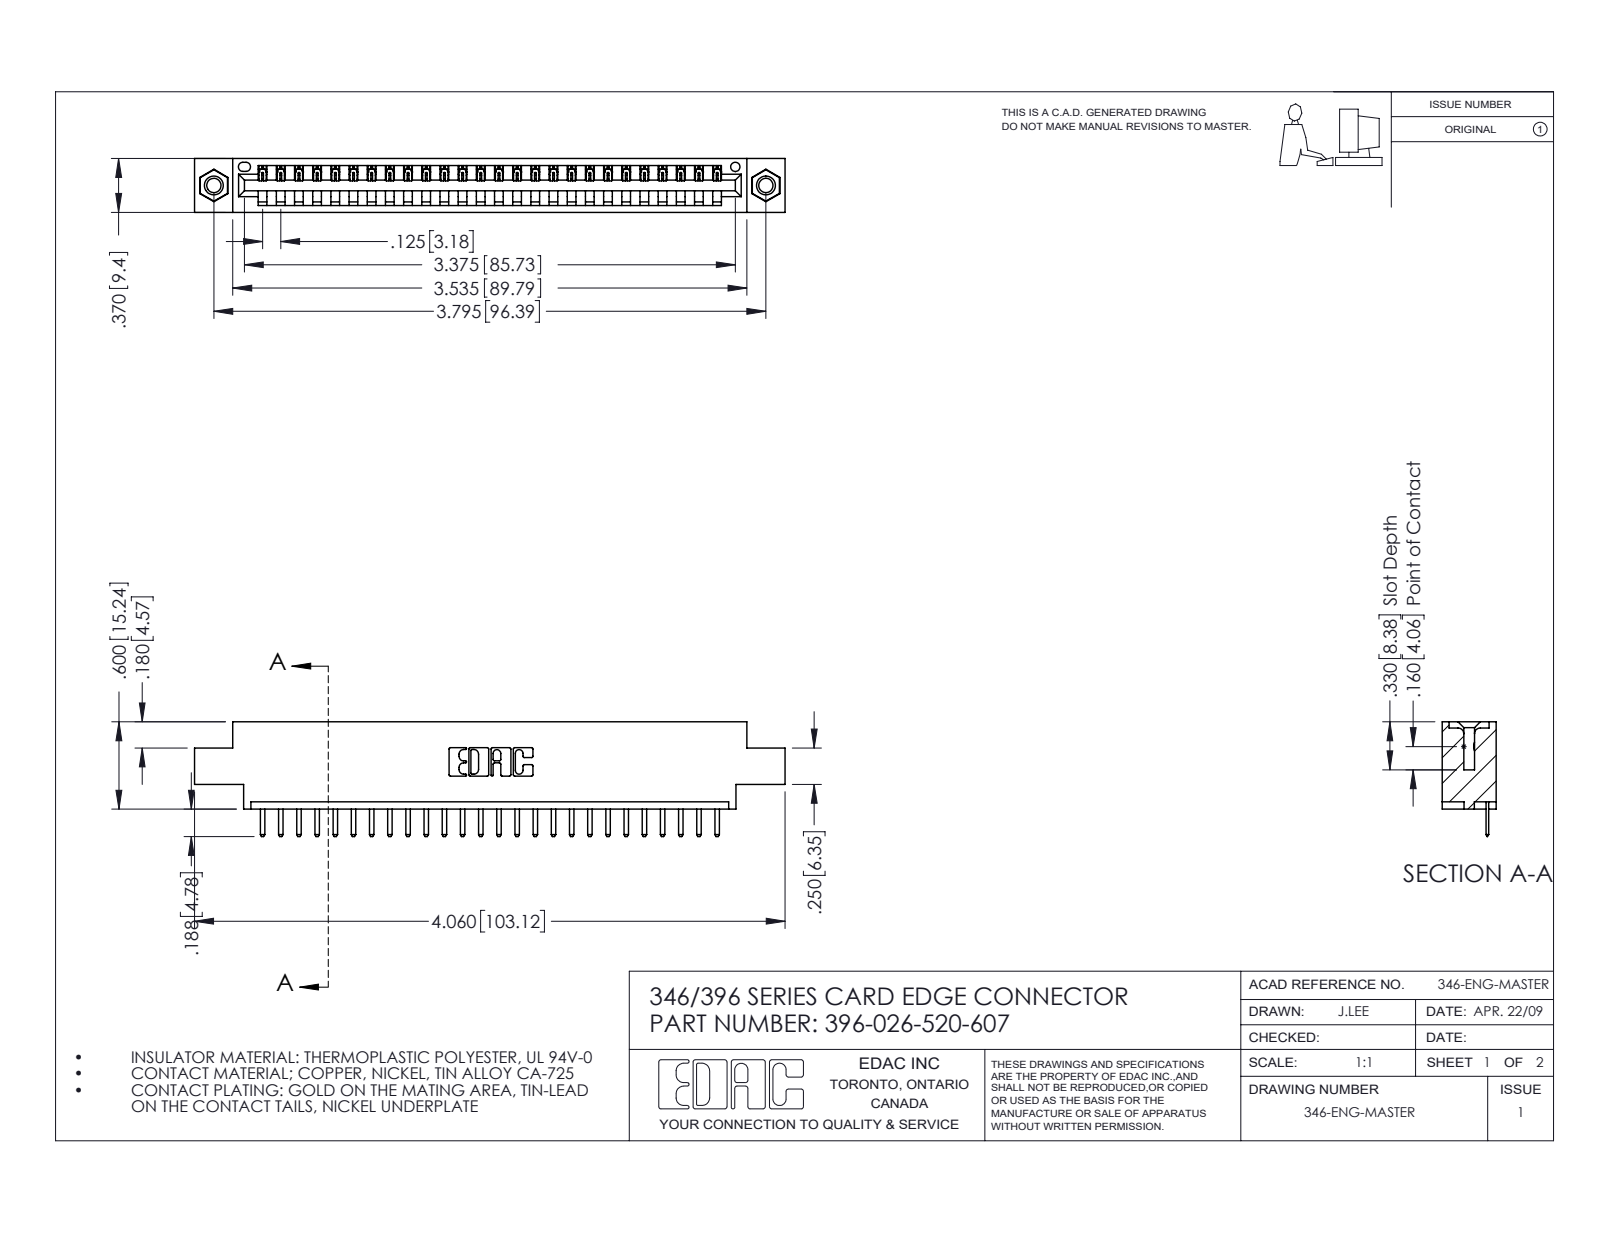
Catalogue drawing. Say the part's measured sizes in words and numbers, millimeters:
The part is named "346 Part_0.170 Offset - 0.156 Dia-TI; 396-026-520-607; 345-292-001_345-293-120; 345-250-001_345-250-005-103". Its 3-D file was written by "SolidWorks 2016 (CONFIG_CONTROL_DESIGN)". It is 29 solids with 1798 faces: 1204 planar, 578 cylindrical and 16 other. Overall it measures 103.1 by 20 by 9.4 millimeters. Its volume is 9 520 cubic millimeters and its surface area 11 670 square millimeters. Round holes: 2 of diameter 2.5, 2 of diameter 3.2, 2 of diameter 4, 1 of diameter 1.6. Round bosses or shafts: 2 of diameter 3.9. Partial cylindrical surfaces (rounded edges, fillets, slot ends): 54 of radius 0.3, 52 of radius 0.2, 22 of radius 0.3, 6 of radius 0.2, 6 of radius 0.8, 3 of radius 0.7, 2 of radius 0.8, 2 of radius 1. The main face-to-face distances are 1.2, 8.2, 9.4, 6.4, 5.6, 3.8, 2.5, 4.4, 1.8, 7.6. The hole center spacings are 6.2, 91.1, 96.4.
